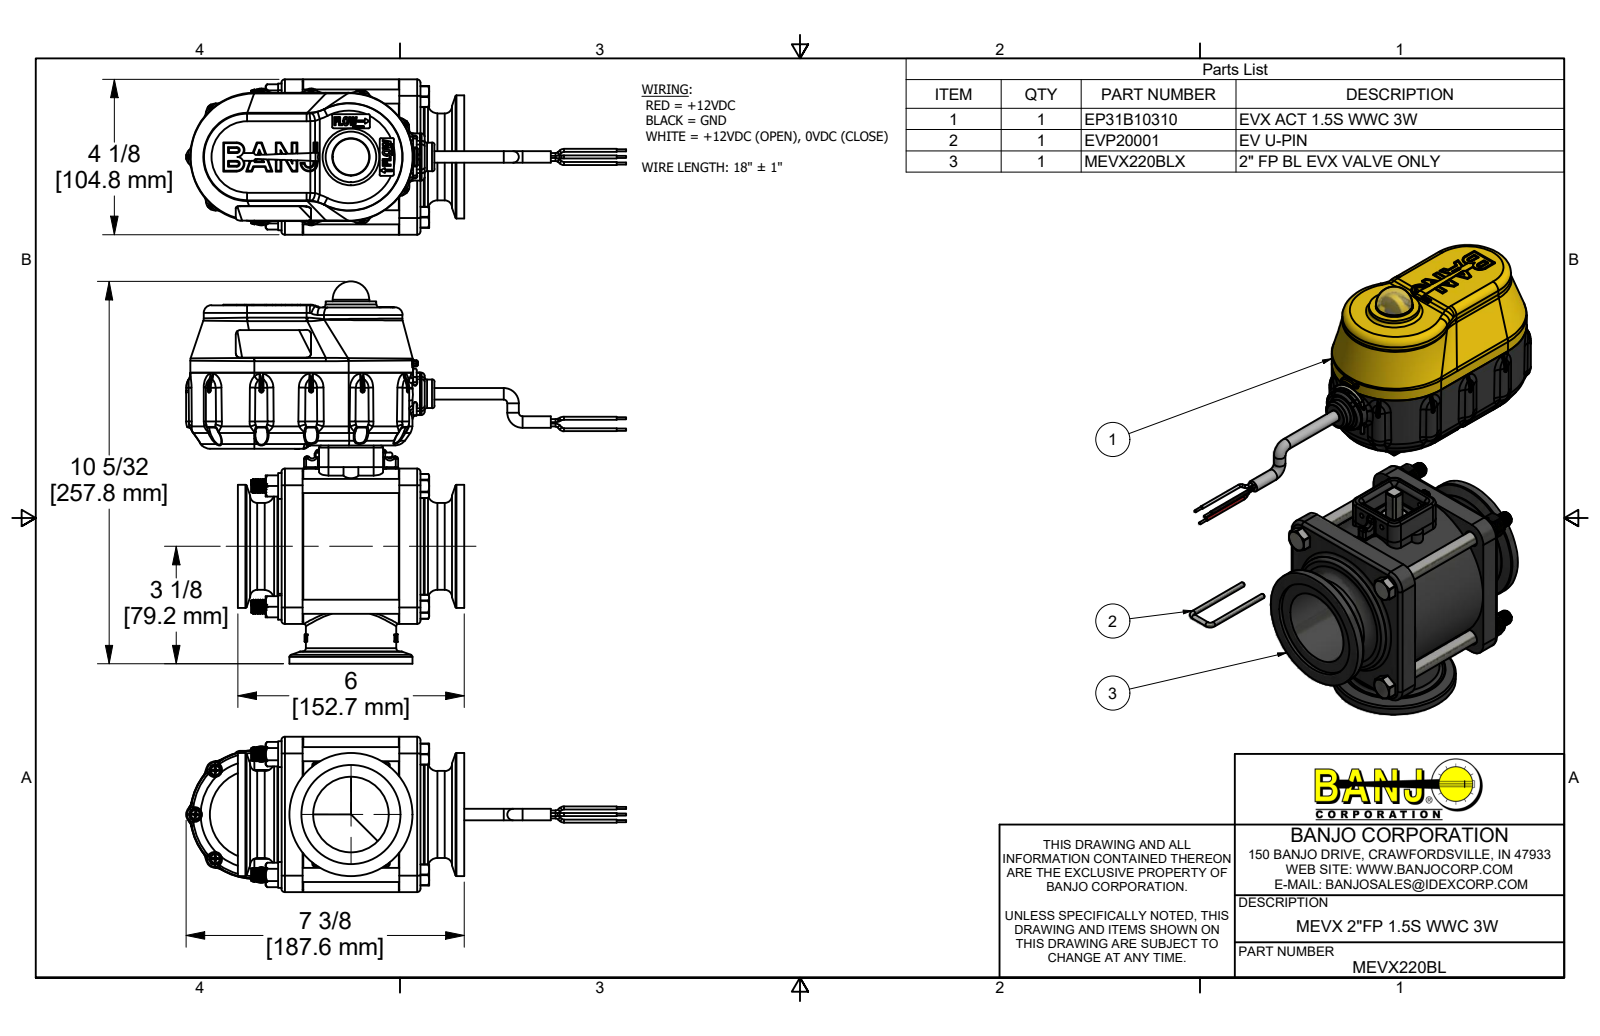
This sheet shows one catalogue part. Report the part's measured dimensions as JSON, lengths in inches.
{"part_name": "MEVX220BL; MEVX220BLX; MEVX25354AB; MEVX25354ABX (+8 more)", "step_written_by": "Autodesk Inventor 2019 (AUTOMOTIVE_DESIGN)", "units": "inches", "bodies": {"solids": 98, "faces": 11669, "planar": 3237, "cylindrical": 3351, "other": 5081}, "overall_size": [11.685, 10.15, 4.125], "volume_in3": 77.63, "surface_area_in2": 757.3, "round_holes": [[0.095, 11], [0.15, 11], [0.08, 7], [0.107, 4], [0.126, 4], [0.136, 4], [0.148, 4], [0.15, 4], [0.17, 4], [0.307, 4], [0.385, 4], [0.438, 4]], "round_bosses_or_shafts": [[0.324, 60], [0.25, 17], [0.08, 15], [0.14, 11], [0.108, 11], [0.085, 11], [0.058, 6], [0.375, 5]], "partial_cylinders_radius": [[0.013, 180], [0.04, 145], [0.01, 84], [0.02, 72], [0.005, 53], [0.03, 38], [0.06, 28], [0.08, 28]], "face_to_face_distances": [0.1, 2.565, 0.06, 0.729, 0.645, 3.045, 2.485, 0.56, 3.13, 0.085], "hole_center_spacings": [2.265, 2.715, 3.204, 1.662, 1.774, 2.458, 2.69, 2.73]}
